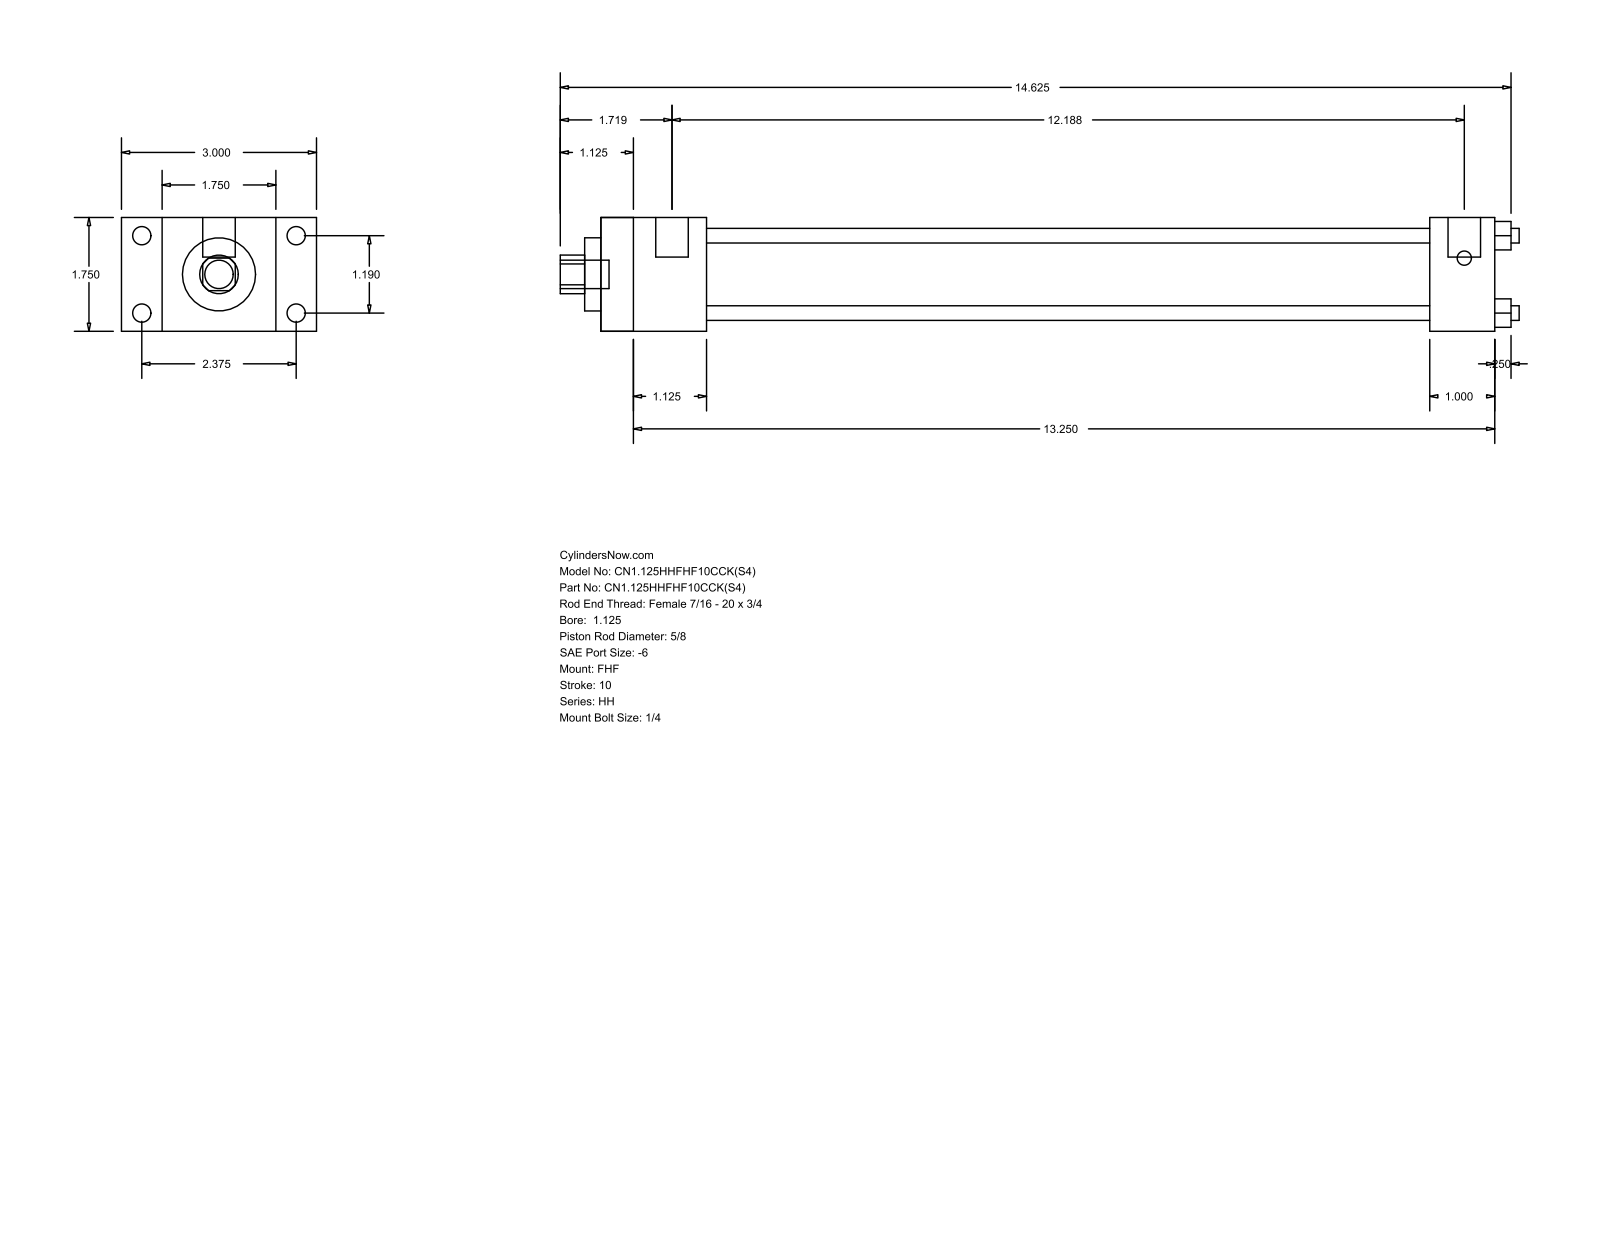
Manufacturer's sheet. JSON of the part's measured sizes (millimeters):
{"part_name": "HH_FHF__0112_0.625", "step_written_by": "GSSL Pune (CONFIG_CONTROL_DESIGN)", "units": "millimeters", "bodies": {"solids": 0, "faces": 88, "planar": 60, "cylindrical": 28, "other": 0}, "overall_size": [374.65, 76.2, 44.45], "round_holes": [[5.71, 4], [15.88, 1], [28.57, 1], [34.92, 1]], "round_bosses_or_shafts": [[7.14, 4], [5.56, 4], [12.7, 2], [11.11, 1]], "partial_cylinders_radius": [[7.54, 1]], "face_to_face_distances": [44.46, 15.87, 60.33, 41.27, 76.2, 349.24, 307.97, 323.85, 282.58, 25.39], "hole_center_spacings": [21.37, 30.22, 42.74]}
